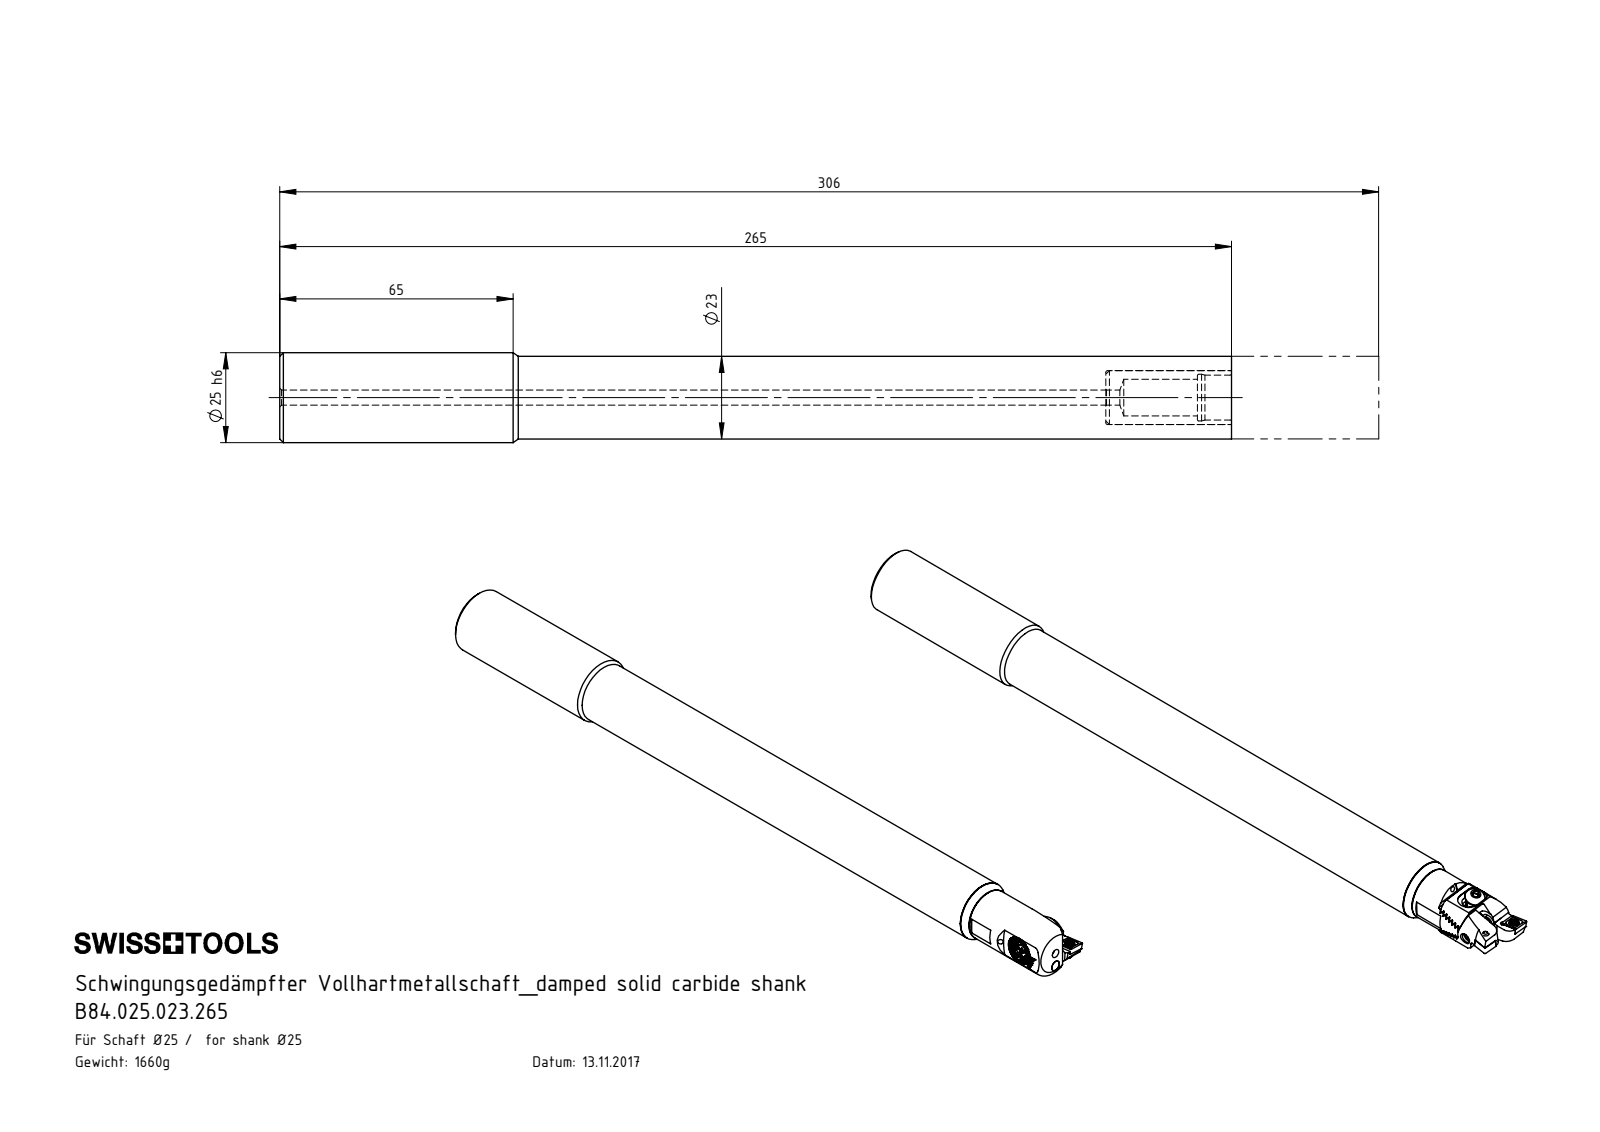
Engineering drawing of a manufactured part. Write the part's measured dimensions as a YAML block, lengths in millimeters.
part_name: "D23-D20.HP4.003_A; DIN 3771 - 11x1_x; F20-ER1.101.006_A; F20-BG2.011.004_A (+8 more)"
step_written_by: "SolidWorks 2017 (CONFIG_CONTROL_DESIGN)"
units: millimeters
bodies: {solids: 19, faces: 831, planar: 344, cylindrical: 166, other: 321}
overall_size: [306, 25, 25]
volume: 121909
surface_area: 38219
round_holes:
  - {diameter: 2, count: 4}
  - {diameter: 3.3, count: 3}
  - {diameter: 1.6, count: 1}
  - {diameter: 1.9, count: 1}
  - {diameter: 2.05, count: 1}
  - {diameter: 2.5, count: 1}
  - {diameter: 2.8, count: 1}
  - {diameter: 3, count: 1}
  - {diameter: 3.85, count: 1}
  - {diameter: 4, count: 1}
  - {diameter: 4.2, count: 1}
  - {diameter: 4.5, count: 1}
round_bosses_or_shafts:
  - {diameter: 4, count: 2}
  - {diameter: 3.95, count: 2}
  - {diameter: 25, count: 1}
  - {diameter: 23, count: 1}
  - {diameter: 20, count: 1}
  - {diameter: 12, count: 1}
  - {diameter: 10.98, count: 1}
  - {diameter: 10.85, count: 1}
partial_cylinders:
  - {radius: 0.21, count: 6}
  - {radius: 0.36, count: 5}
  - {radius: 0.3, count: 2}
  - {radius: 0.5, count: 2}
  - {radius: 2, count: 2}
  - {radius: 3, count: 2}
  - {radius: 5, count: 2}
  - {radius: 0.36, count: 1}
face_to_face_distances: [265, 3, 268, 38, 230, 35, 6, 303.5, 73.5, 38.5]
hole_center_spacings: [5.6, 7, 12.6, 14]
